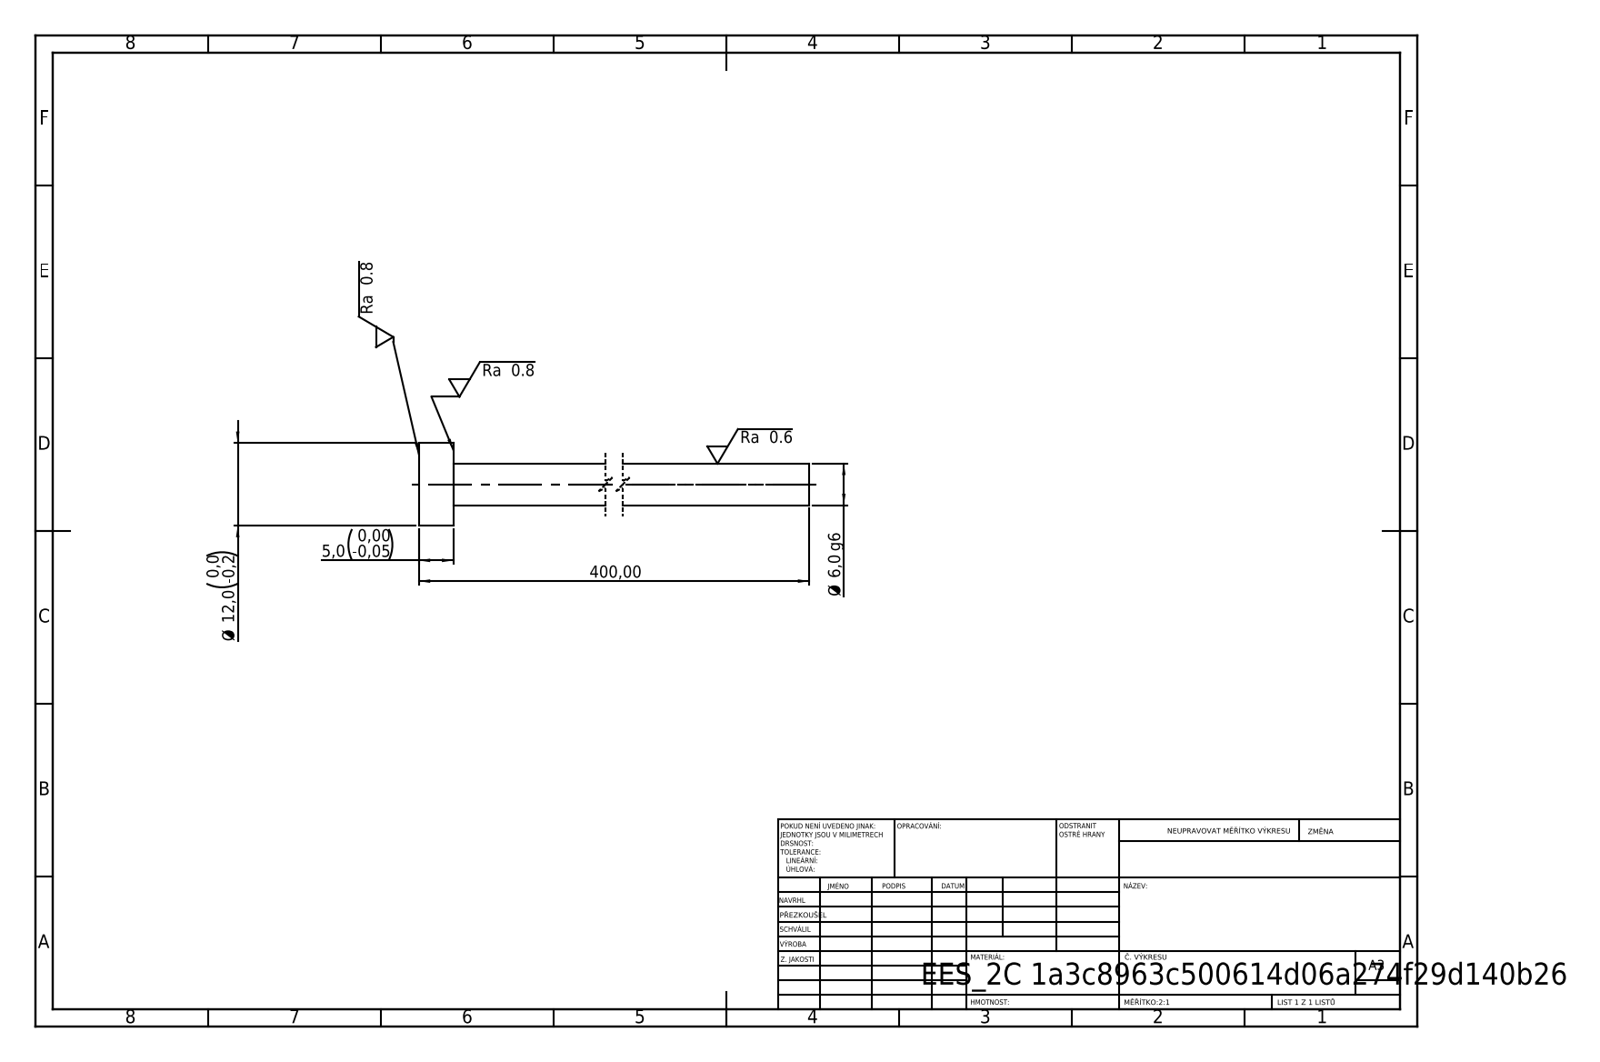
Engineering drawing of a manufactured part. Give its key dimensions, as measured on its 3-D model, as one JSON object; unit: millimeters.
{"step_written_by": "SolidWorks 2019 (CONFIG_CONTROL_DESIGN)", "units": "millimeters", "bodies": {"solids": 1, "faces": 7, "planar": 3, "cylindrical": 4, "other": 0}, "overall_size": [400, 12, 12], "volume_mm3": 11734, "surface_area_mm2": 7860, "round_bosses_or_shafts": [[12, 1], [6, 1]], "face_to_face_distances": [5, 400, 395]}
